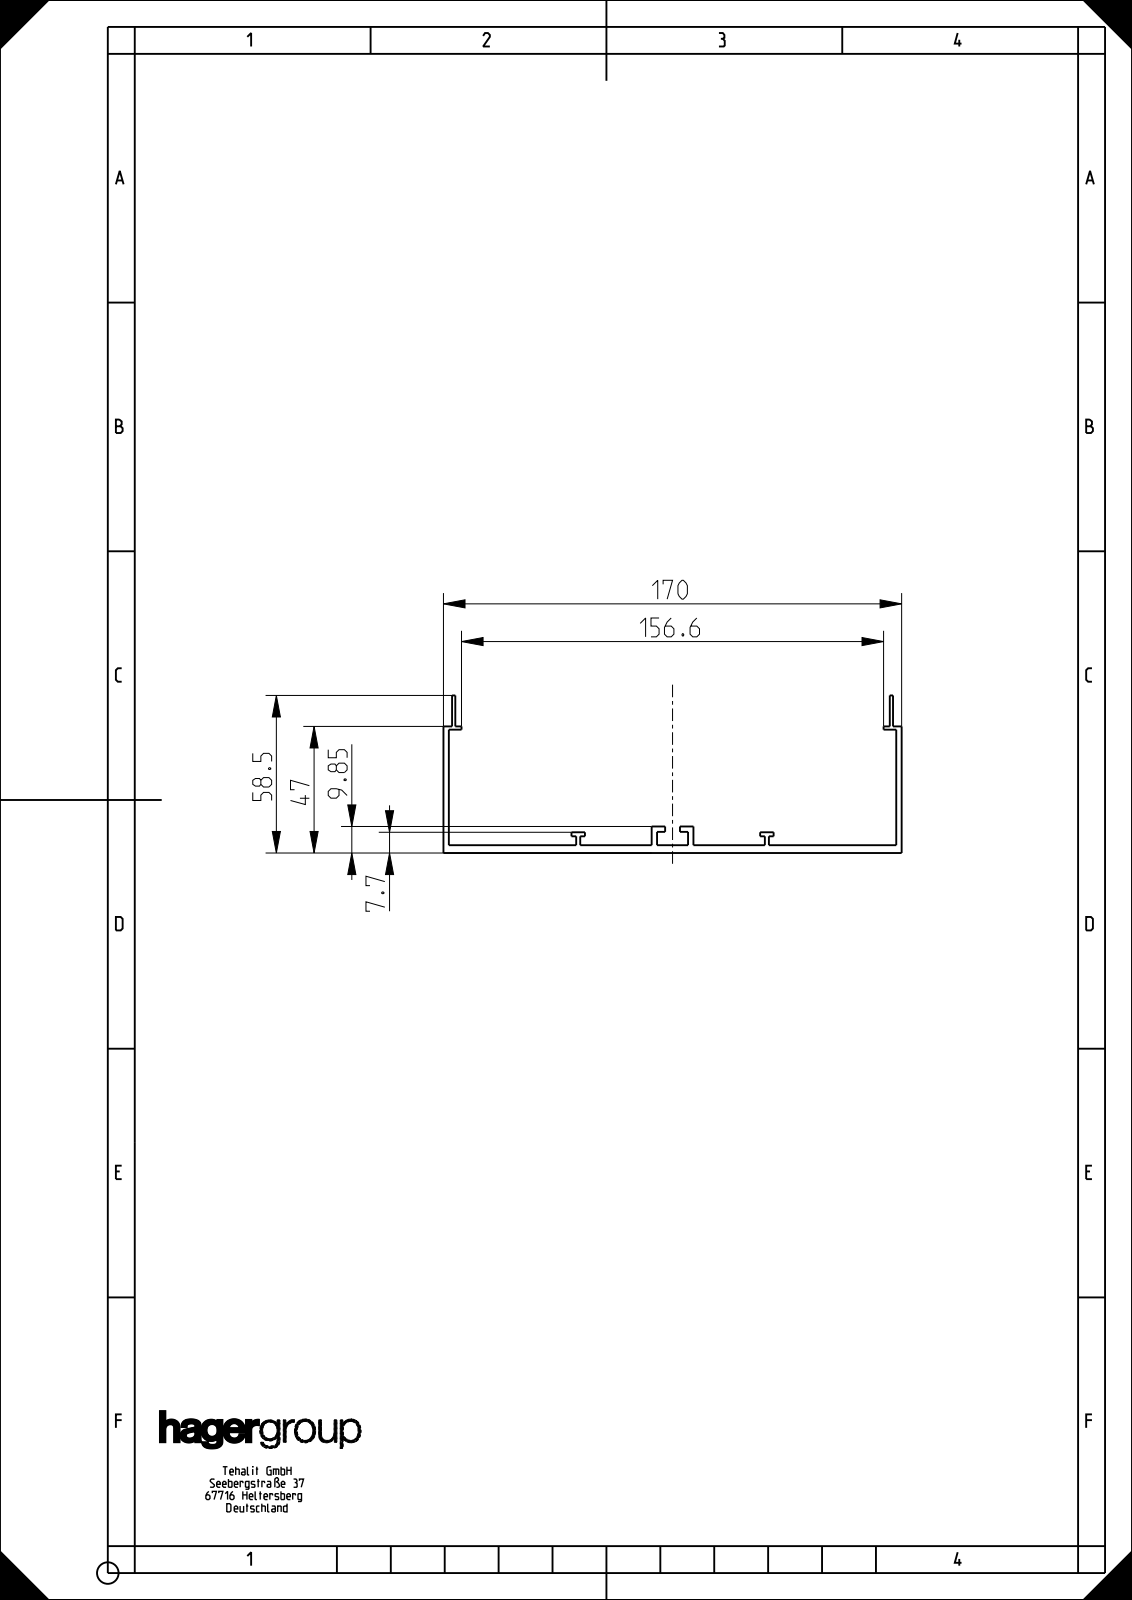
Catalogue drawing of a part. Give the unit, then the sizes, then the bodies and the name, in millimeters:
Units: millimetres
Overall size (bounding box): 2000 × 170 × 58.5
Partial cylindrical surfaces — rounded edges, fillets, slot ends (radius × count): R2.3 ×80, R3.25 ×40
Main face-to-face distances: 2.9, 2, 168, 1.2, 170, 166, 163.6, 77.25, 90.75, 3.2
Volume: 1 526 000 mm³ · Surface area: 1 323 000 mm²
Bodies: 1 solid, 1970 faces (1810 planar, 160 cylindrical, 0 other)
Part name (STEP PRODUCT): BRN651701KUN
STEP written by: CREO PARAMETRIC BY PTC INC, 2022162 (AUTOMOTIVE_DESIGN)
